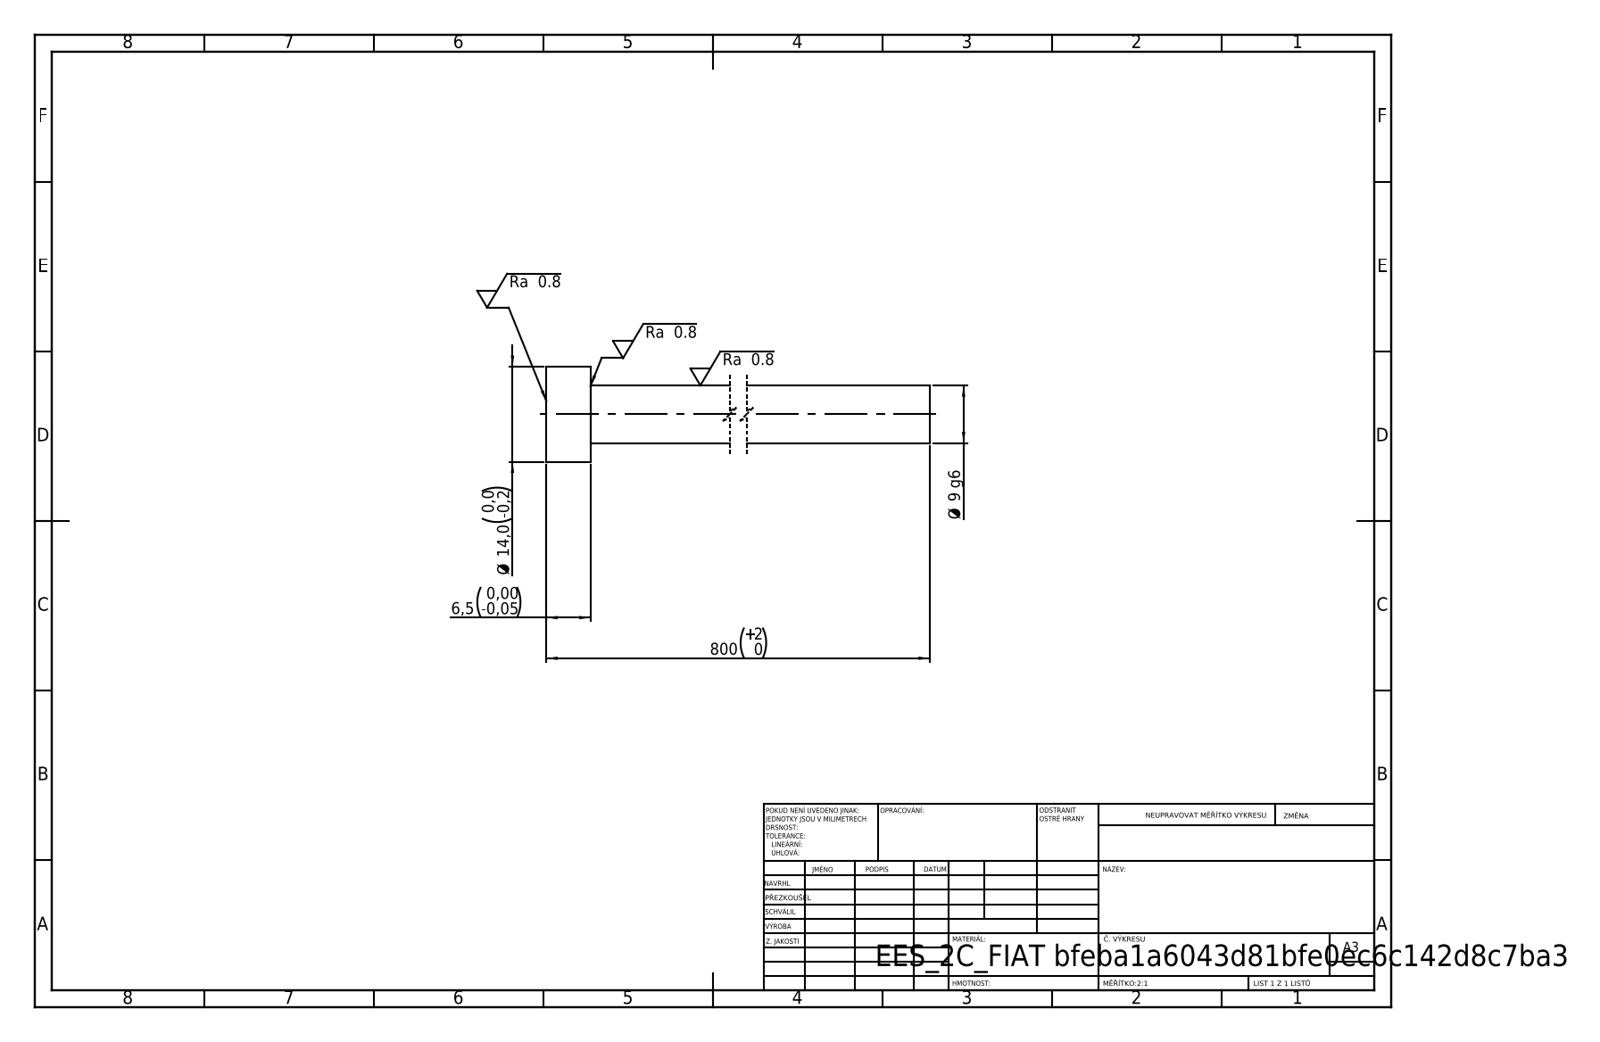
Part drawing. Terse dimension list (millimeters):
written by: SolidWorks 2019 (CONFIG_CONTROL_DESIGN)
unit: mm
bodies: 1 solid, 7 faces (3 planar, 4 cylindrical, 0 other)
size: 800 × 14 × 14
volume: 46 028 mm³; area: 21 783 mm²
bosses: 1× ⌀14, 1× ⌀8.5
face distances: 6.5, 800, 793.5
